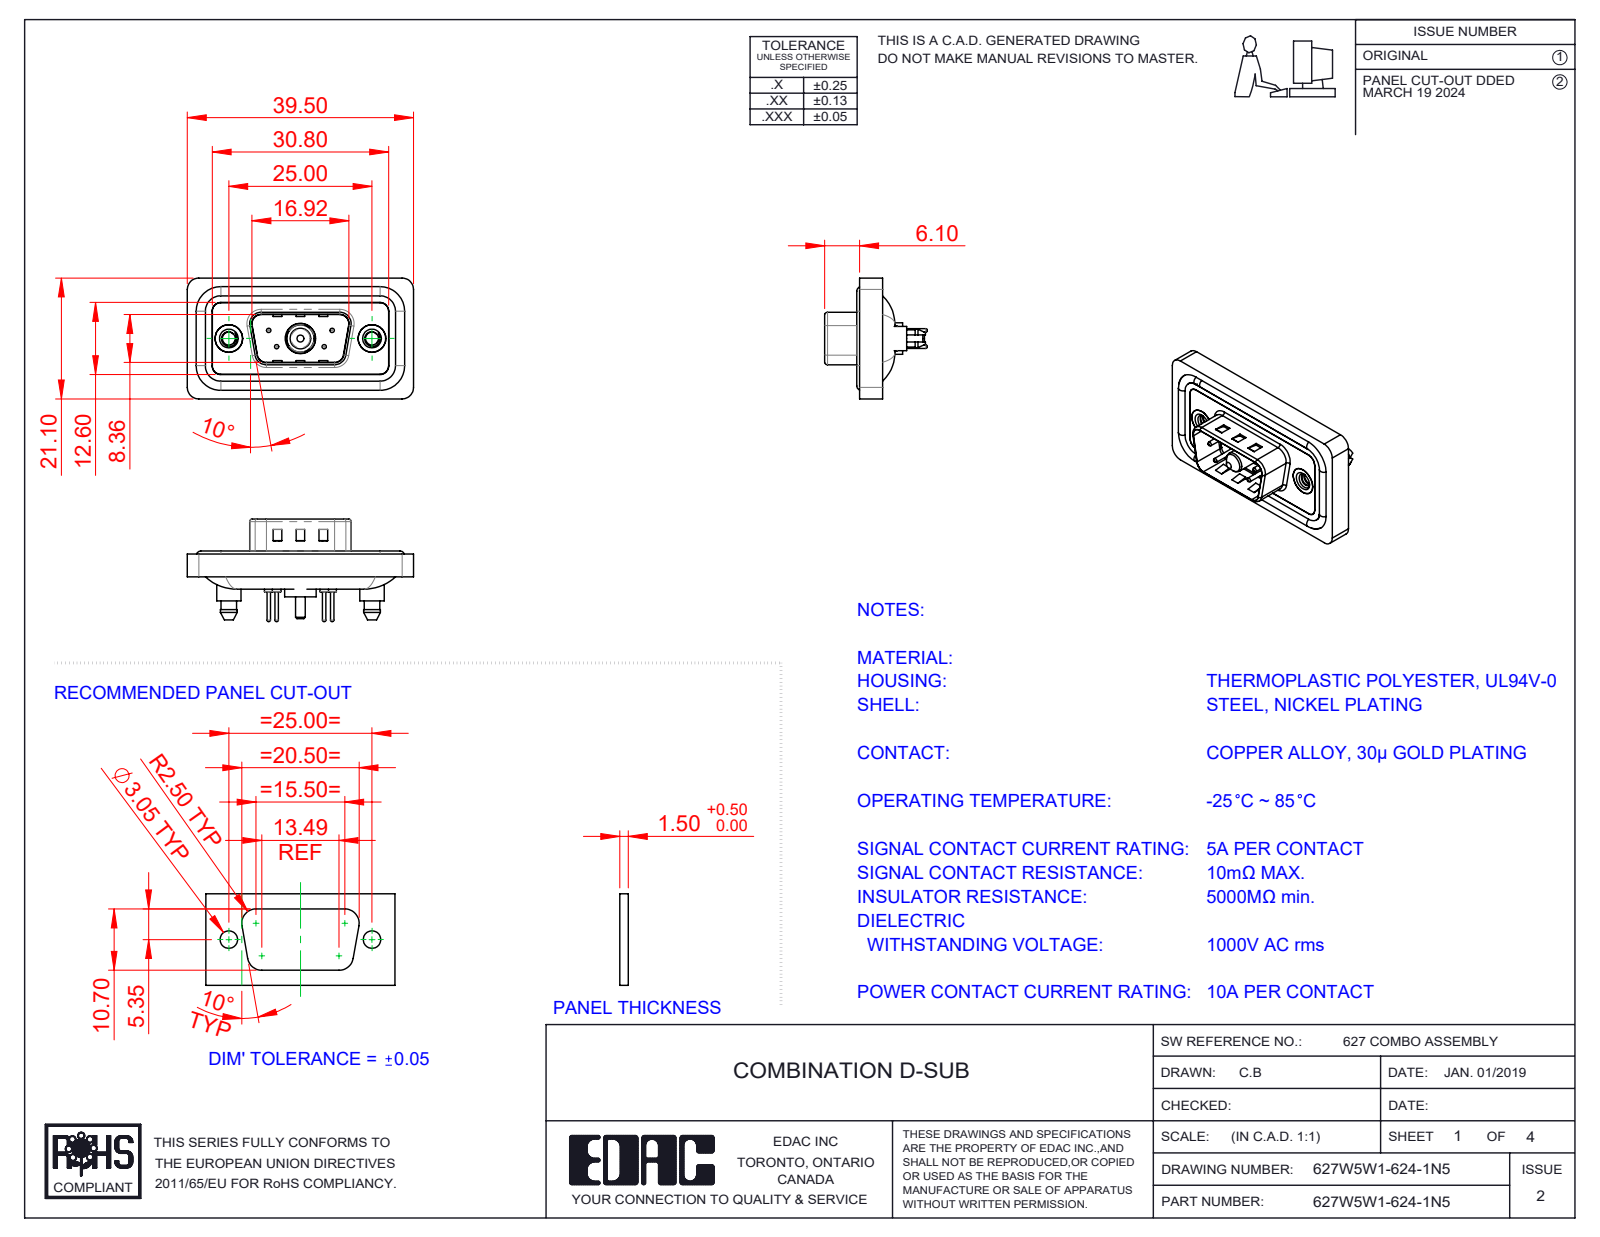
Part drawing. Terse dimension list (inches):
name: Power Pin_10A S; 627Combo Housing_5W1; 627Combo Shell Front_09 Contacts; 627Combo Contact Row 2_24 (+5 more)
written by: SolidWorks 2023 (CONFIG_CONTROL_DESIGN)
unit: in
bodies: 13 solids, 648 faces (199 planar, 287 cylindrical, 162 other)
size: 1.555 × 0.831 × 0.705
volume: 0.275 in³; area: 11.26 in²
holes: 4× ⌀0.03, 4× ⌀0.063, 4× ⌀0.079, 2× ⌀0.089, 2× ⌀0.157, 2× ⌀0.189, 2× ⌀0.197, 1× ⌀0.191, 1× ⌀0.209
bosses: 4× ⌀0.063, 4× ⌀0.059, 4× ⌀0.024, 2× ⌀0.213, 2× ⌀0.193, 2× ⌀0.167, 1× ⌀0.217, 1× ⌀0.205
rounds: 24× R0.059, 18× R0.079, 10× R0.063, 8× R0.02, 4× R0.01, 4× R0.024, 4× R0.026, 4× R0.035
face distances: 0.016, 0.043, 0.114, 0.063, 0.059, 0.122, 0.02, 0.098, 0.157, 0.028
hole spacings: 0.124, 0.225, 0.28, 0.492, 0.713, 0.173, 0.173, 0.327
